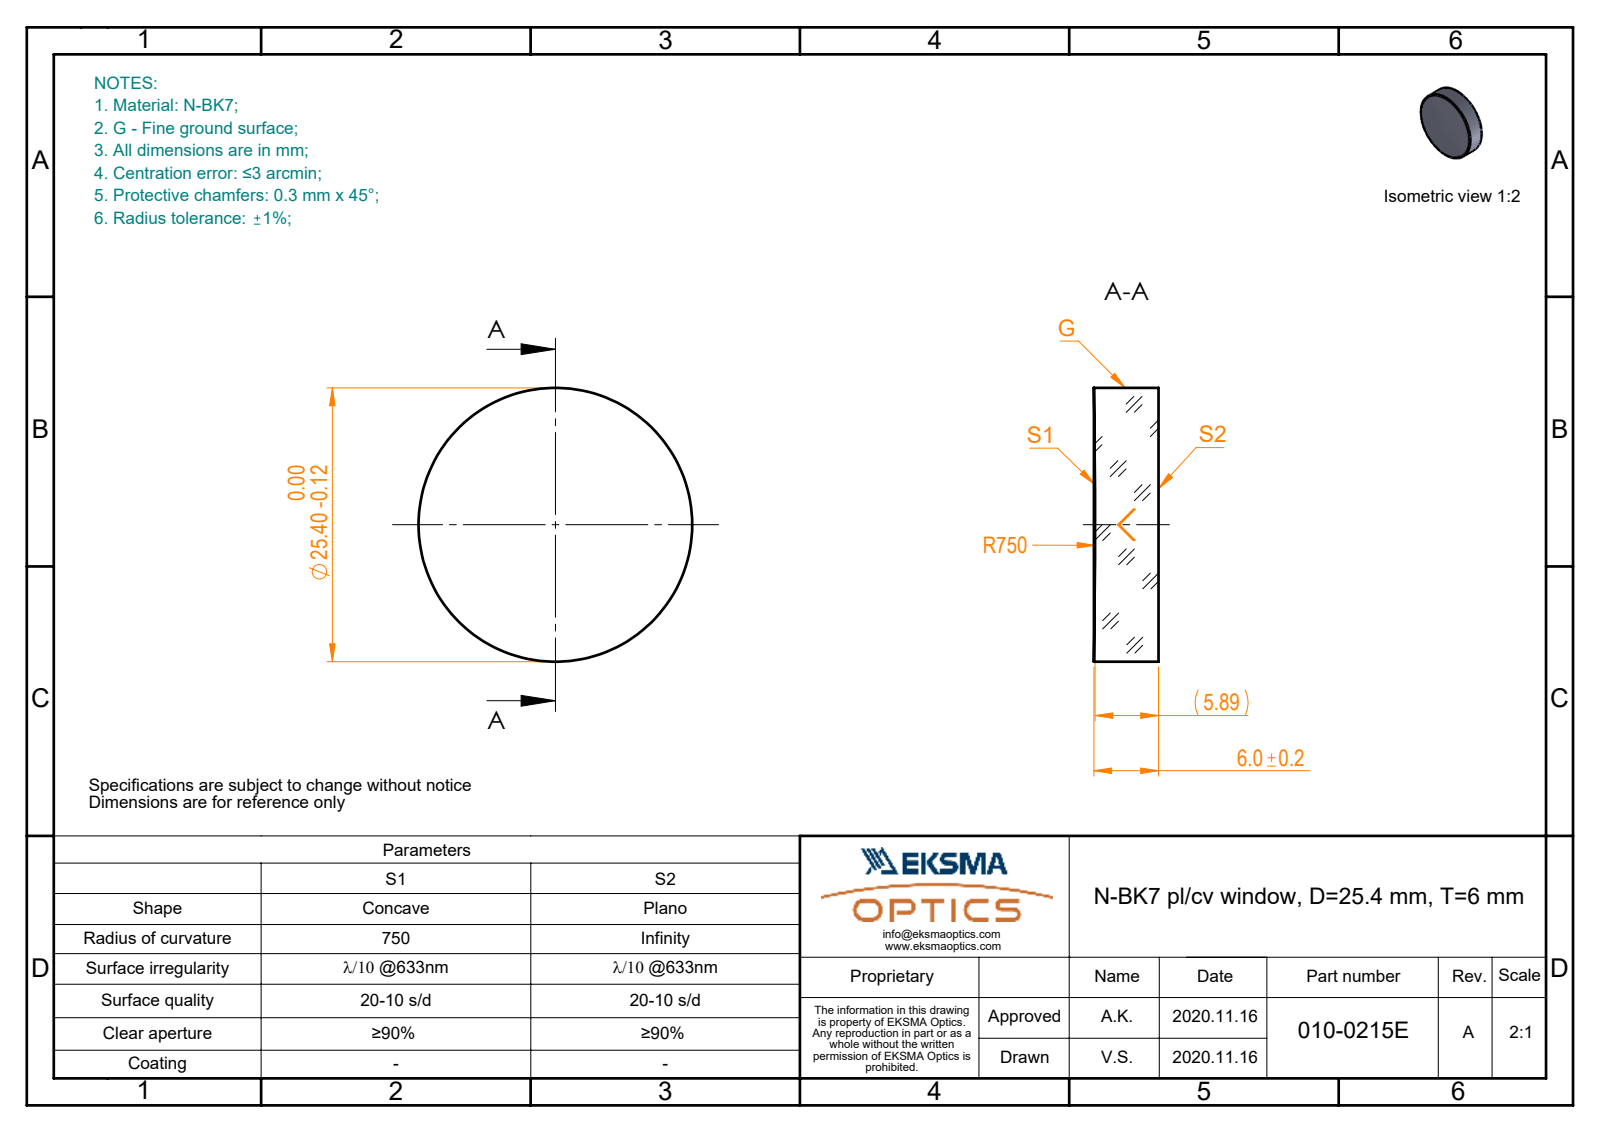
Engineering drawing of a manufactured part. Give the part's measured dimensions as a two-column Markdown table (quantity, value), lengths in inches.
| quantity | value |
| --- | --- |
| part name | 010-0215E_N-BK7_PCV_window |
| STEP written by | SolidWorks 2019 (CONFIG_CONTROL_DESIGN) |
| units | inches |
| bodies | 1 solid, 5 faces (1 planar, 2 cylindrical, 2 other) |
| overall size | 1 × 1 × 0.236 |
| volume | 0.184 in³ |
| surface area | 2.313 in² |
| round bosses / shafts (diameter × count) | 1 × 1 |
